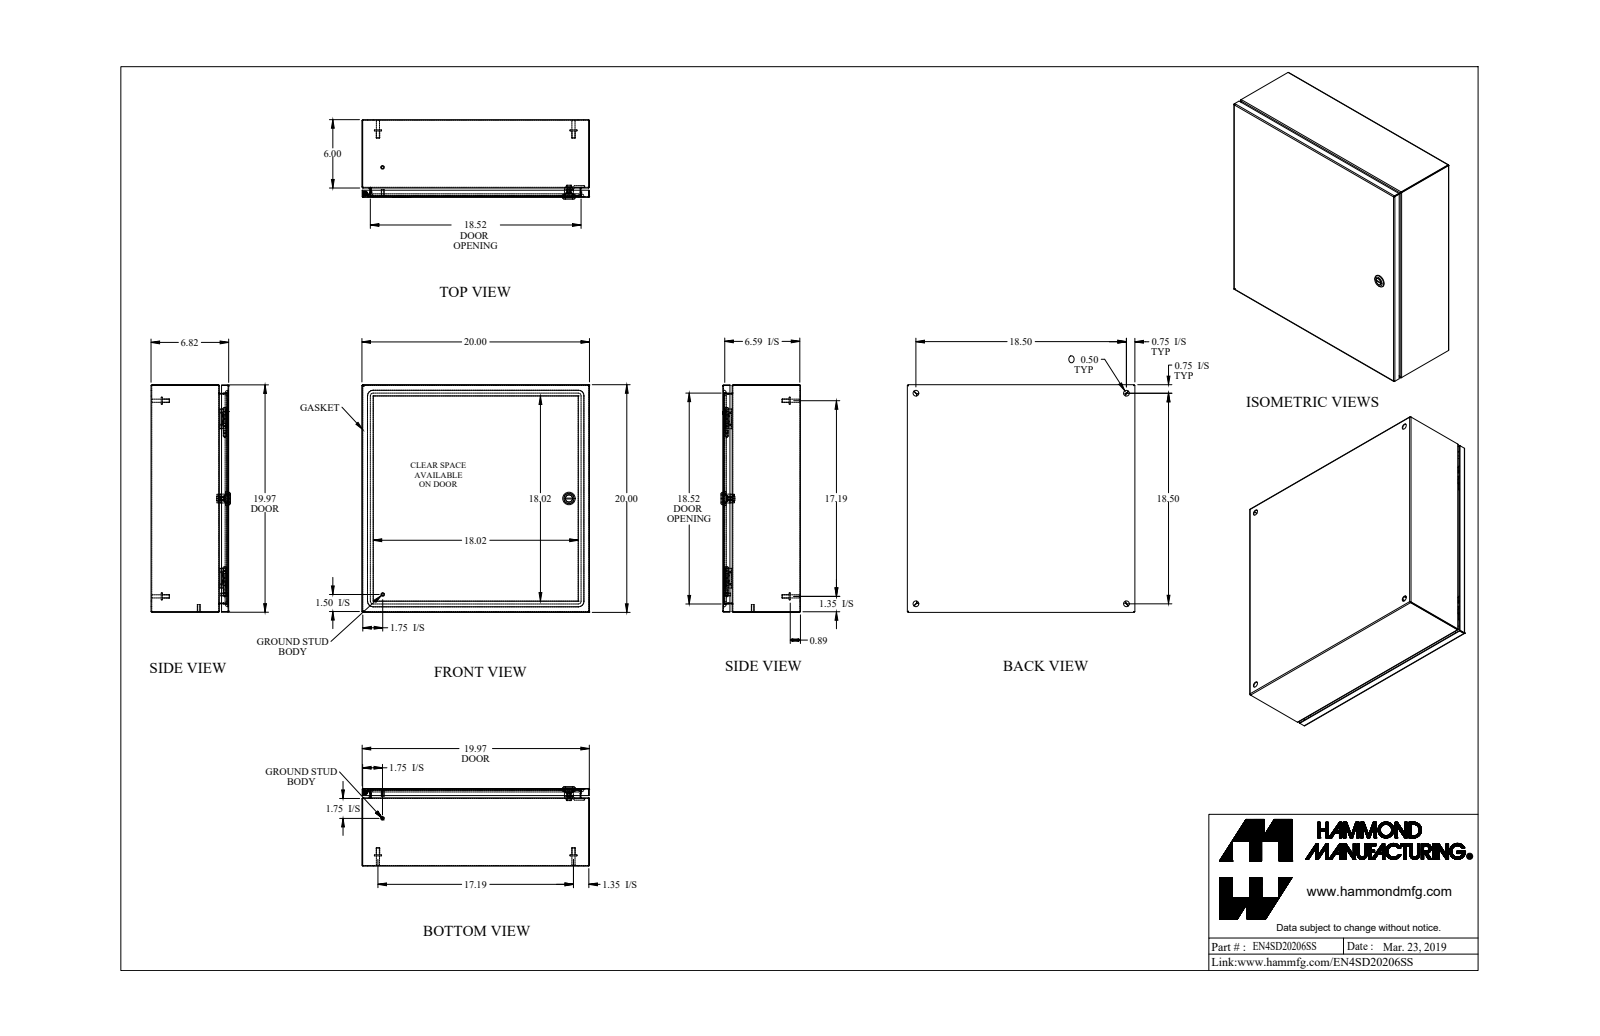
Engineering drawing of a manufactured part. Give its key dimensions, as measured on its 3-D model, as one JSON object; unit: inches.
{"part_name": "EN4SD20206SS_Default", "step_written_by": "SolidWorks 2019 (CONFIG_CONTROL_DESIGN)", "units": "inches", "bodies": {"solids": 22, "faces": 656, "planar": 303, "cylindrical": 211, "other": 142}, "overall_size": [20, 20, 6.982], "volume_in3": 89.76, "surface_area_in2": 3052, "round_holes": [[0.5, 5], [0.172, 1], [0.197, 1], [0.24, 1], [0.242, 1], [0.387, 1], [0.63, 1], [0.768, 1]], "round_bosses_or_shafts": [[0.313, 6], [0.625, 5], [0.275, 4], [0.25, 2], [1.1, 1], [0.785, 1], [0.525, 1], [0.455, 1]], "partial_cylinders_radius": [[0.029, 21], [0.086, 21], [0.188, 12], [0.006, 4], [0.062, 4], [0.25, 4], [0.499, 4], [0.125, 2]], "face_to_face_distances": [0.057, 6.765, 19.943, 6.708, 6.822, 19.886, 20, 0.822, 5.943, 0.749], "hole_center_spacings": [18.5, 9.31, 19.742, 26.163]}
